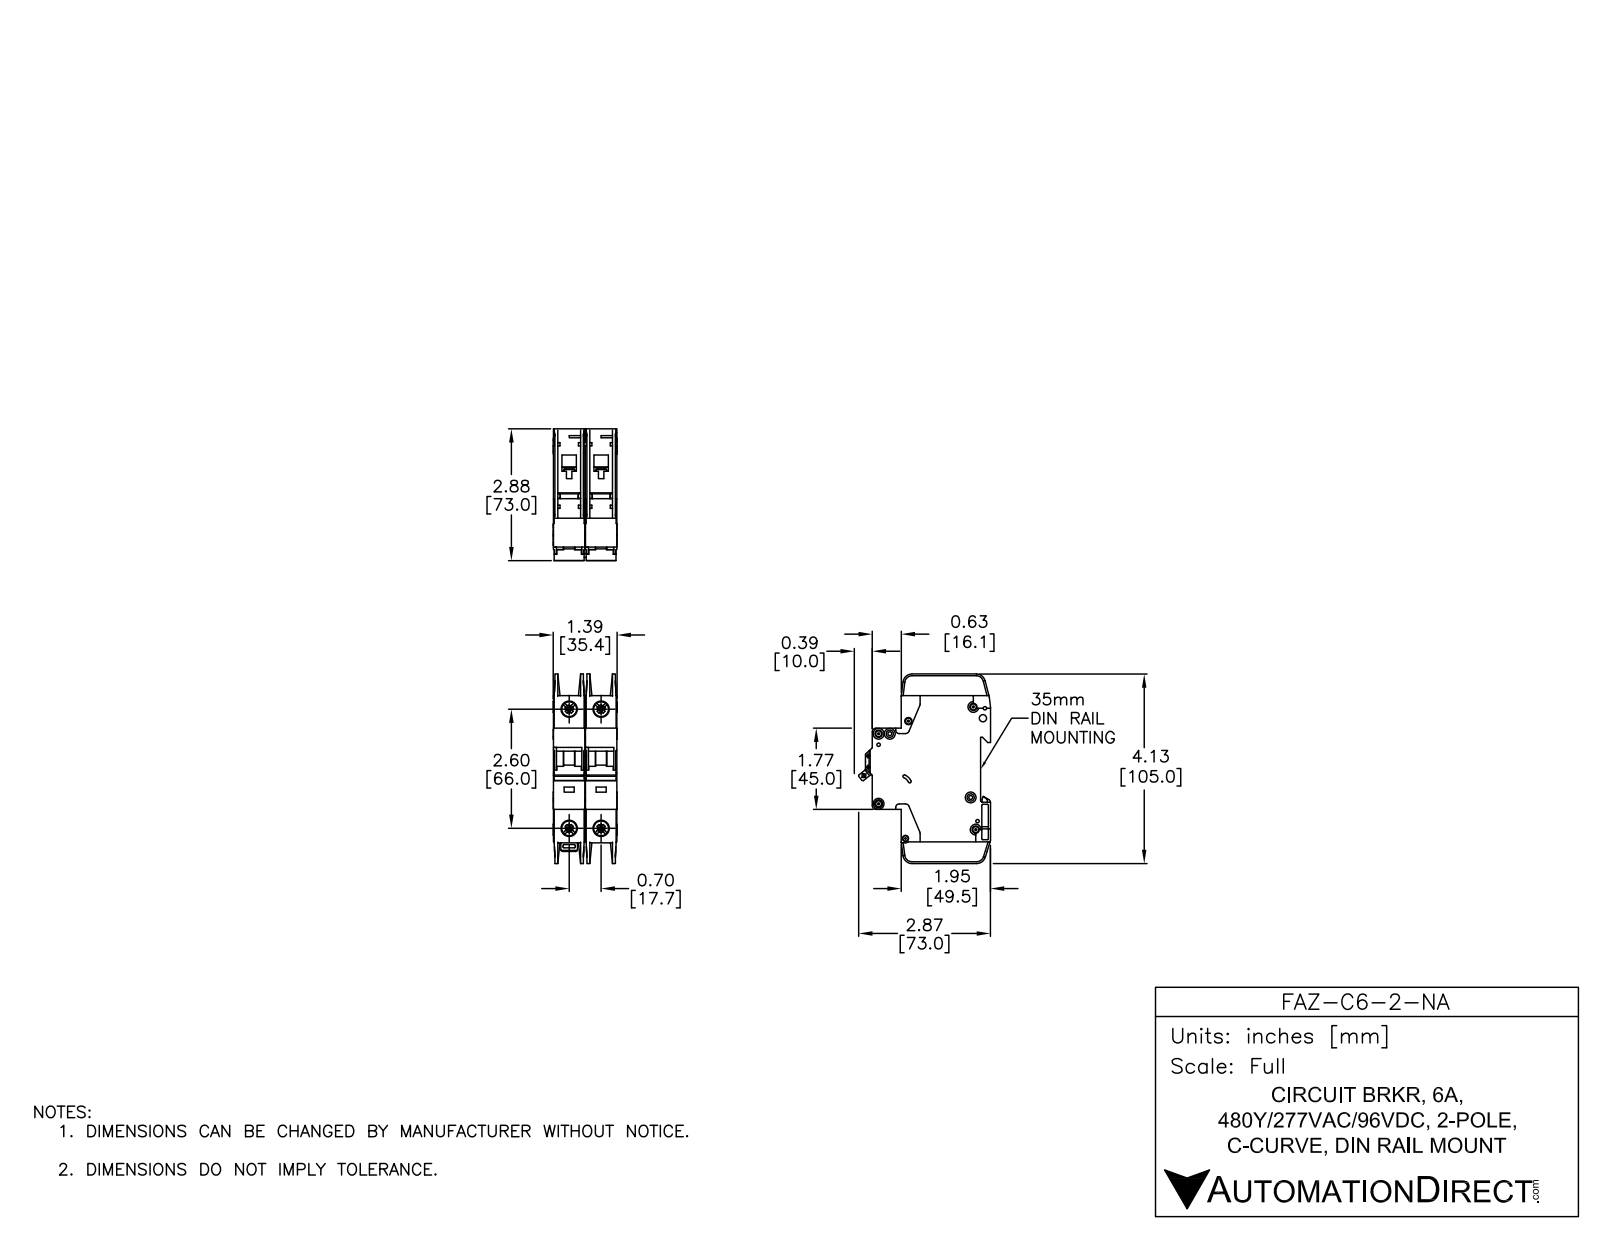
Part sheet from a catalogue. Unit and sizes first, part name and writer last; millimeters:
Units: millimetres
Overall size (bounding box): 105 × 73.04 × 35.4
Round holes (diameter × count): ⌀3.6 ×7, ⌀7.15 ×4, ⌀8.2 ×4, ⌀1.09 ×2, ⌀1.5 ×2, ⌀4 ×2, ⌀1.9 ×1, ⌀2.15 ×1, ⌀2.2 ×1, ⌀2.55 ×1, ⌀3.3 ×1, ⌀3.4 ×1
Round bosses / shafts (diameter × count): ⌀6 ×7, ⌀2.5 ×2
Partial cylindrical surfaces — rounded edges, fillets, slot ends (radius × count): R0.25 ×47, R0.5 ×24, R1 ×18, R2 ×12, R5 ×5, R1.8 ×4, R4 ×4, R0.2 ×2
Main face-to-face distances: 17.7, 17.5, 0.7, 15.05, 2.45, 1.75, 15.75, 13.3, 35.2, 17
Hole centre spacings: 6.2, 17.7, 66, 68.33, 5.19, 6.1, 8.19, 8.56
Volume: 155 390 mm³ · Surface area: 49 479 mm²
Bodies: 6 solids, 1568 faces (818 planar, 526 cylindrical, 224 other)
Part name (STEP PRODUCT): FAZ-C6-2-NA
STEP written by: SolidWorks 2014 (AUTOMOTIVE_DESIGN)
